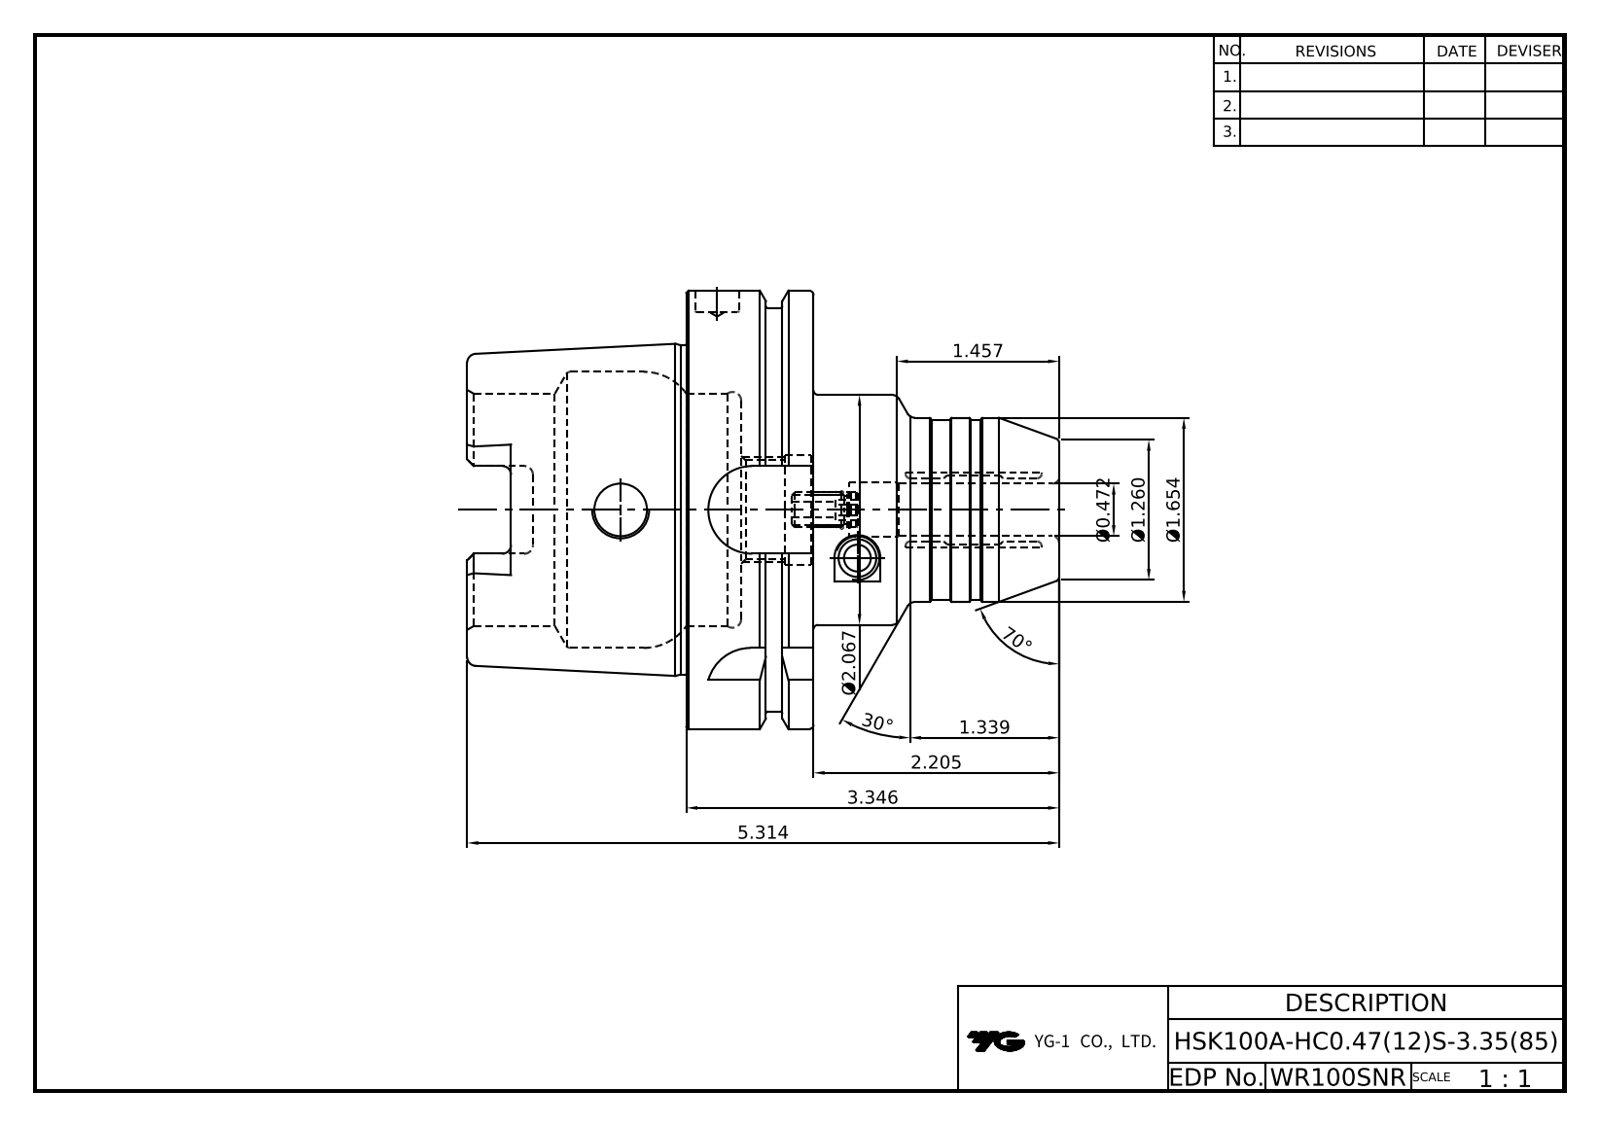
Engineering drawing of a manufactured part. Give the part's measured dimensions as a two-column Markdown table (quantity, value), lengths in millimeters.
| quantity | value |
| --- | --- |
| part name | HSK100A-HC12S-85 |
| STEP written by | Autodesk Inventor 2022 (AUTOMOTIVE_DESIGN) |
| units | millimeters |
| bodies | 1 solid, 126 faces (38 planar, 39 cylindrical, 49 other) |
| overall size | 135 × 100 × 100 |
| volume | 337 472 mm³ |
| surface area | 58 622 mm² |
| round holes (diameter × count) | 12 × 2, 6.92 × 1, 10 × 1, 12.6 × 1, 22.38 × 1, 25 × 1, 53 × 1, 63 × 1 |
| round bosses / shafts (diameter × count) | 100 × 1, 92 × 1, 75.41 × 1, 52.5 × 1, 42 × 1, 41 × 1 |
| partial cylindrical surfaces (radius × count) | 2 × 6, 4.88 × 4, 10 × 4 |
| main face-to-face distances | 29, 12.5, 16.5, 62.5, 79, 50, 72.5, 135, 85, 56 |
